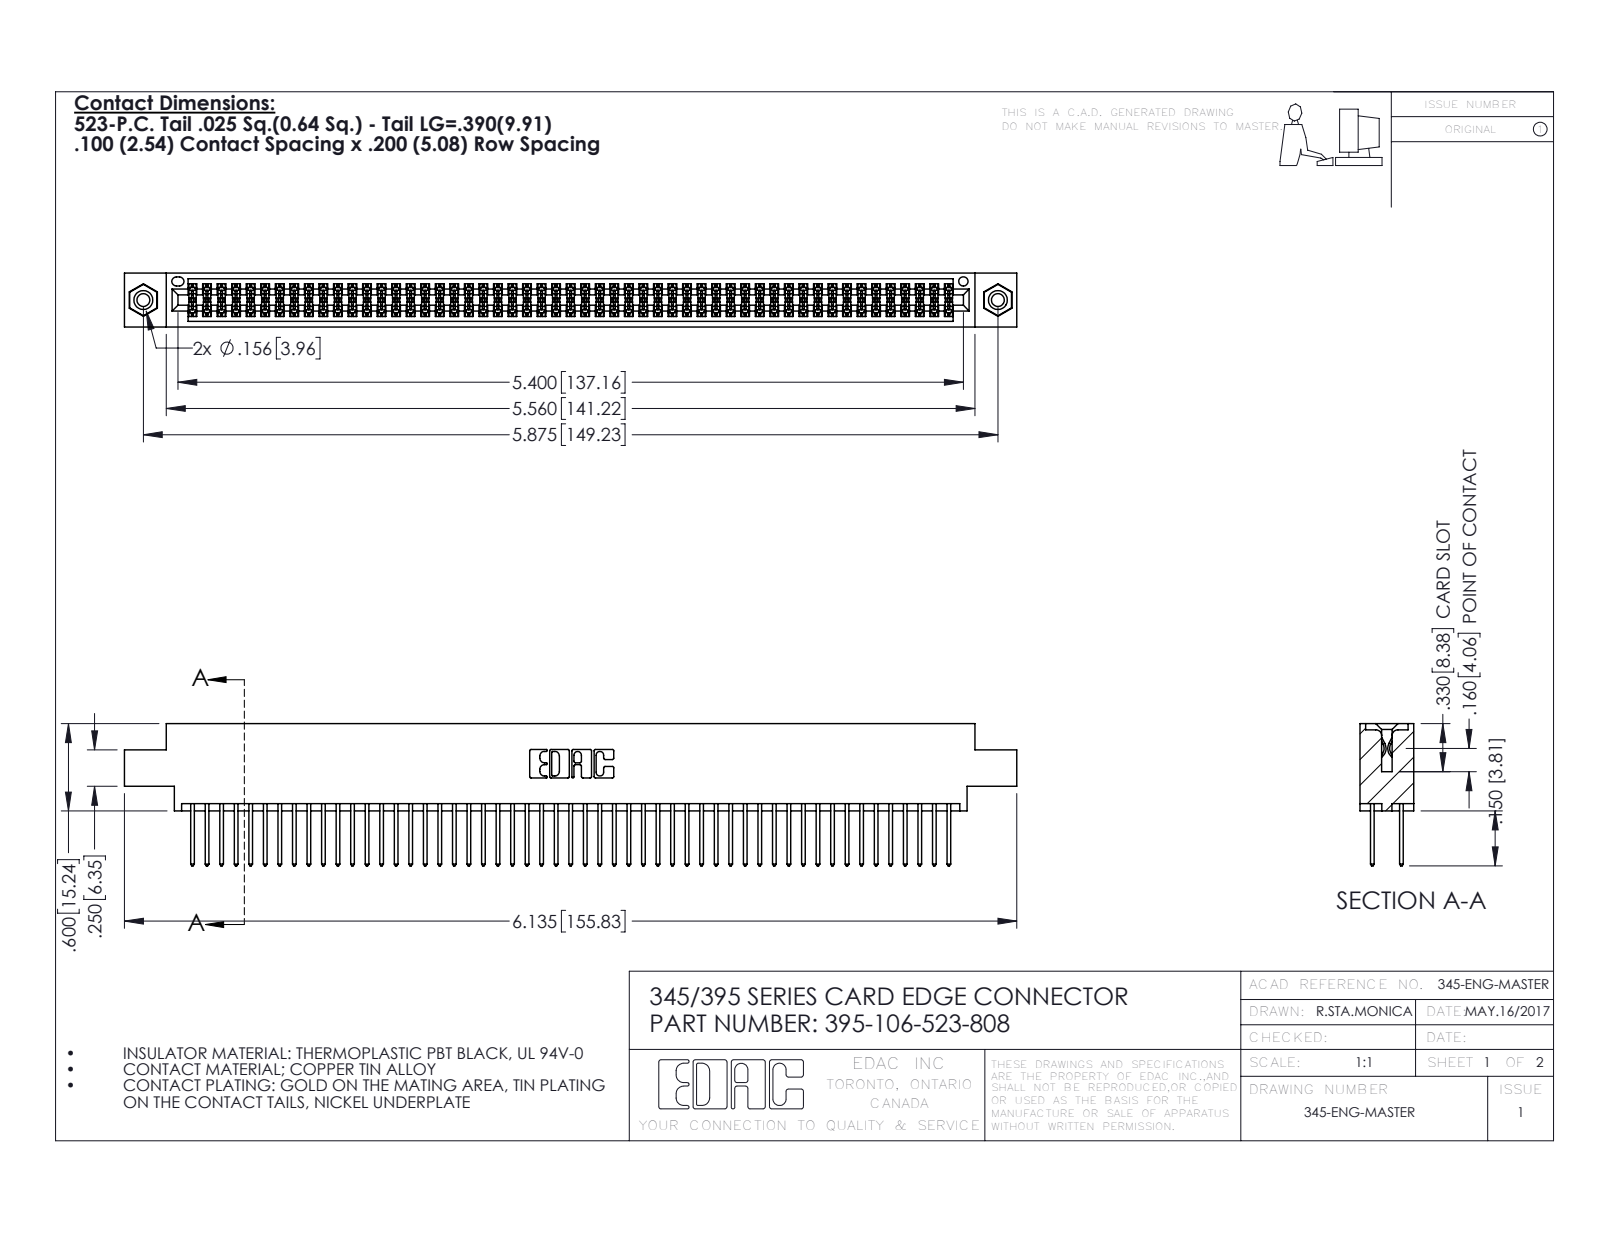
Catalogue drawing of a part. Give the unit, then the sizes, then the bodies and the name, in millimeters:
Units: millimetres
Overall size (bounding box): 155.8 × 24.8 × 9.4
Round holes (diameter × count): ⌀2.3 ×2, ⌀3.2 ×2, ⌀4 ×2, ⌀1.6 ×1
Round bosses / shafts (diameter × count): ⌀3.9 ×2
Partial cylindrical surfaces — rounded edges, fillets, slot ends (radius × count): R0.2 ×159, R0.3 ×106, R0.3 ×22, R0.2 ×6, R0.8 ×6, R0.7 ×3, R0.4 ×2, R0.5 ×2
Main face-to-face distances: 1.8, 7.6, 5.1, 2.5, 6.9, 0.6, 9.4, 5.7, 4.4, 3.8
Hole centre spacings: 6.9, 143.2, 149.2
Volume: 15 300 mm³ · Surface area: 24 010 mm²
Bodies: 109 solids, 5490 faces (3614 planar, 1860 cylindrical, 16 other)
Part name (STEP PRODUCT): 345-292-001_345-293-123; 395-106-523-808; 345-250-001_345-250-003-102; 345 Part_0.170 Offset - 0.156 Dia-TI
STEP written by: SolidWorks 2016 (CONFIG_CONTROL_DESIGN)
